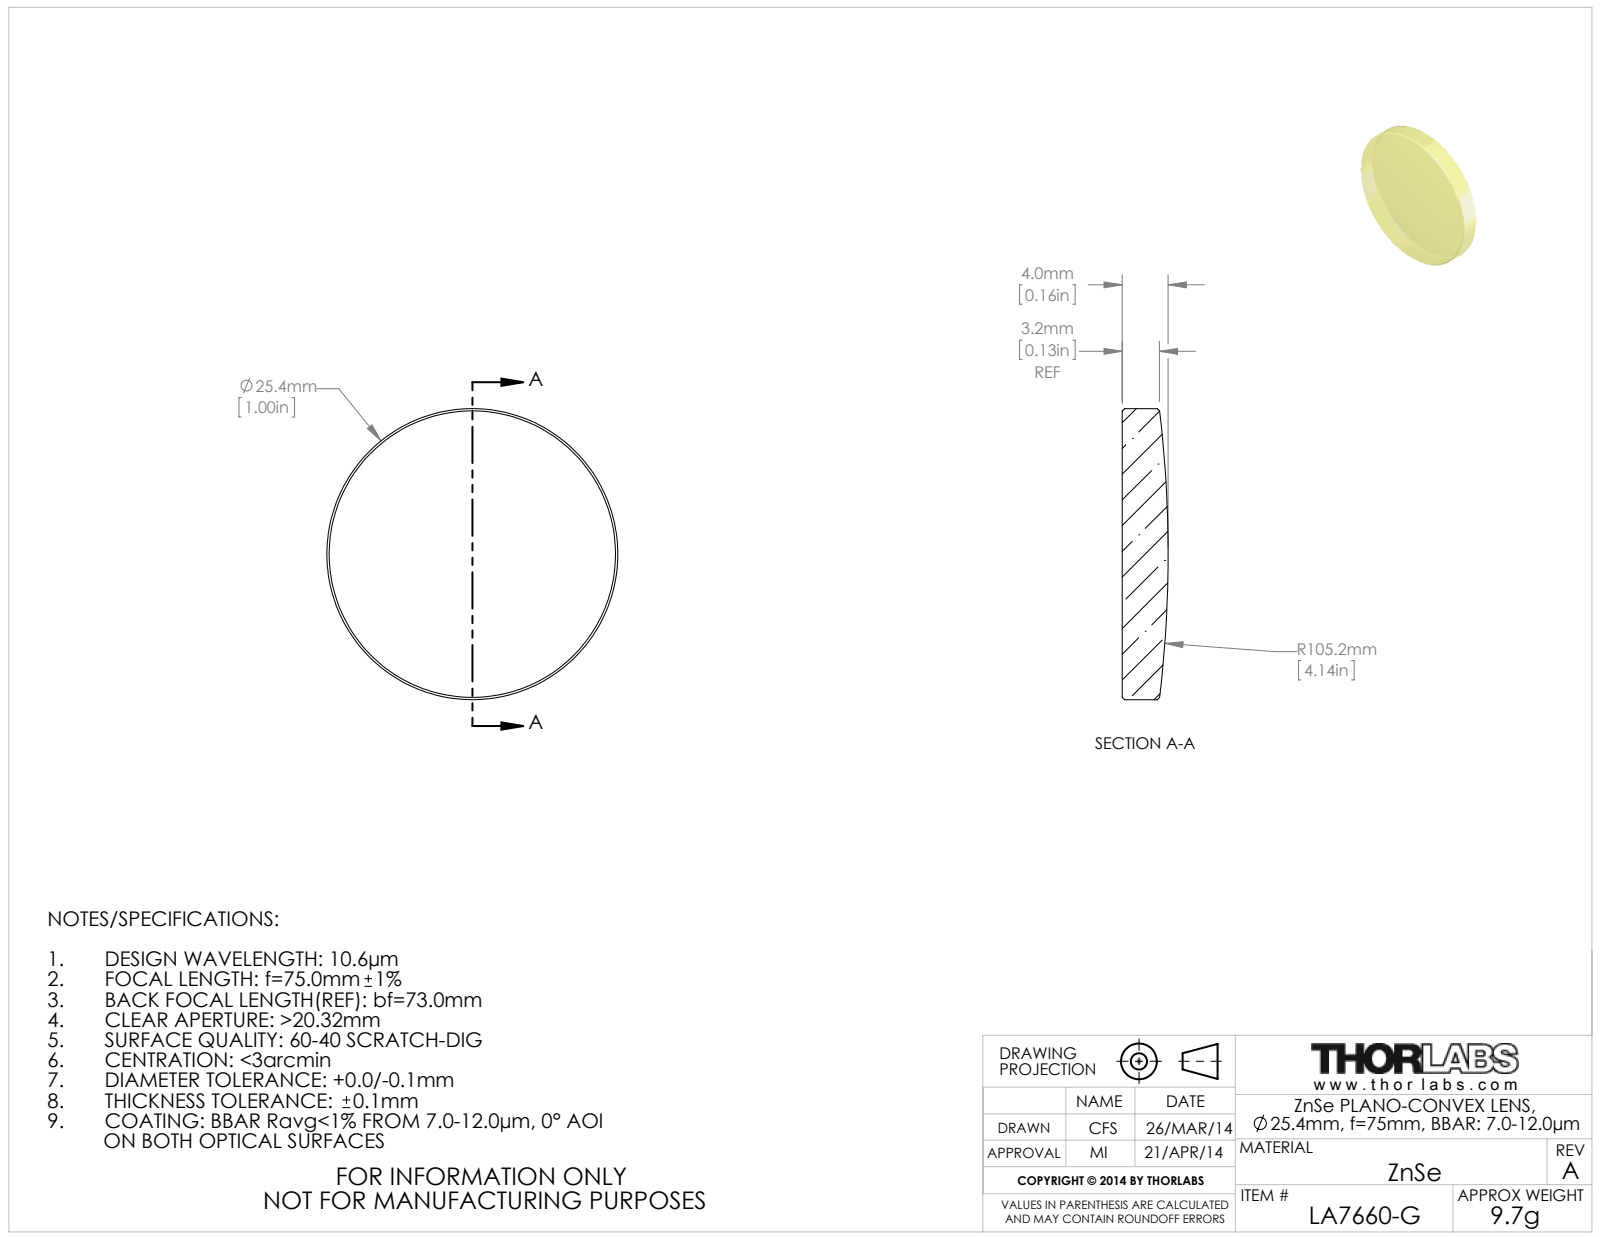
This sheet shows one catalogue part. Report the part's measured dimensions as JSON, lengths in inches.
{"part_name": "TTN023914-E0W", "step_written_by": "SolidWorks 2012 (CONFIG_CONTROL_DESIGN)", "units": "inches", "bodies": {"solids": 1, "faces": 9, "planar": 1, "cylindrical": 2, "other": 6}, "overall_size": [1, 1, 0.157], "volume_in3": 0.112, "surface_area_in2": 1.947, "round_bosses_or_shafts": [[1, 1]]}
